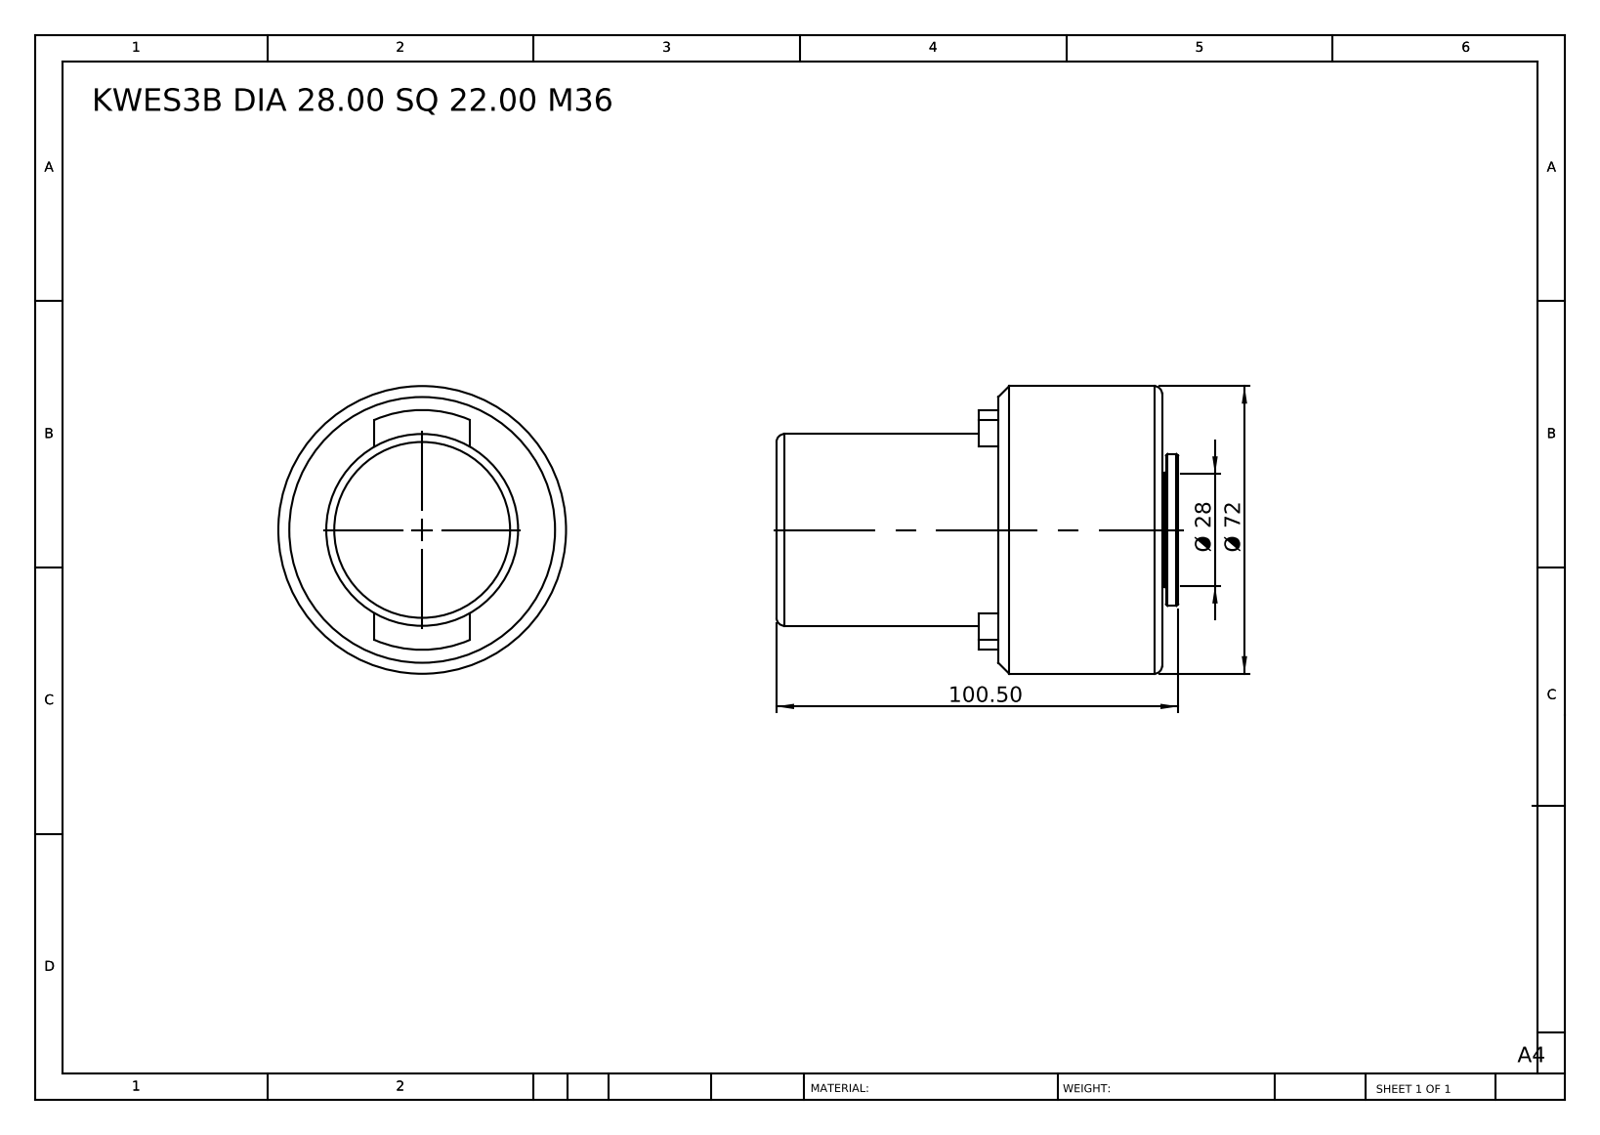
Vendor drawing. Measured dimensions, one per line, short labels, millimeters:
name: KWES3B DIA 28.00 SQ 22.00 1-1-8'''''''' G(BSP)
written by: SolidWorks 2014 (CONFIG_CONTROL_DESIGN)
unit: mm
bodies: 1 solid, 39 faces (12 planar, 13 cylindrical, 14 other)
size: 100.5 × 72 × 72
volume: 247 081 mm³; area: 30 077 mm²
holes: 1× ⌀28
bosses: 1× ⌀72, 1× ⌀48, 1× ⌀38, 1× ⌀28.5
rounds: 1× R30
face distances: 96.5, 55.5, 41, 5, 60.5, 36, 100.5, 45, 40, 4
